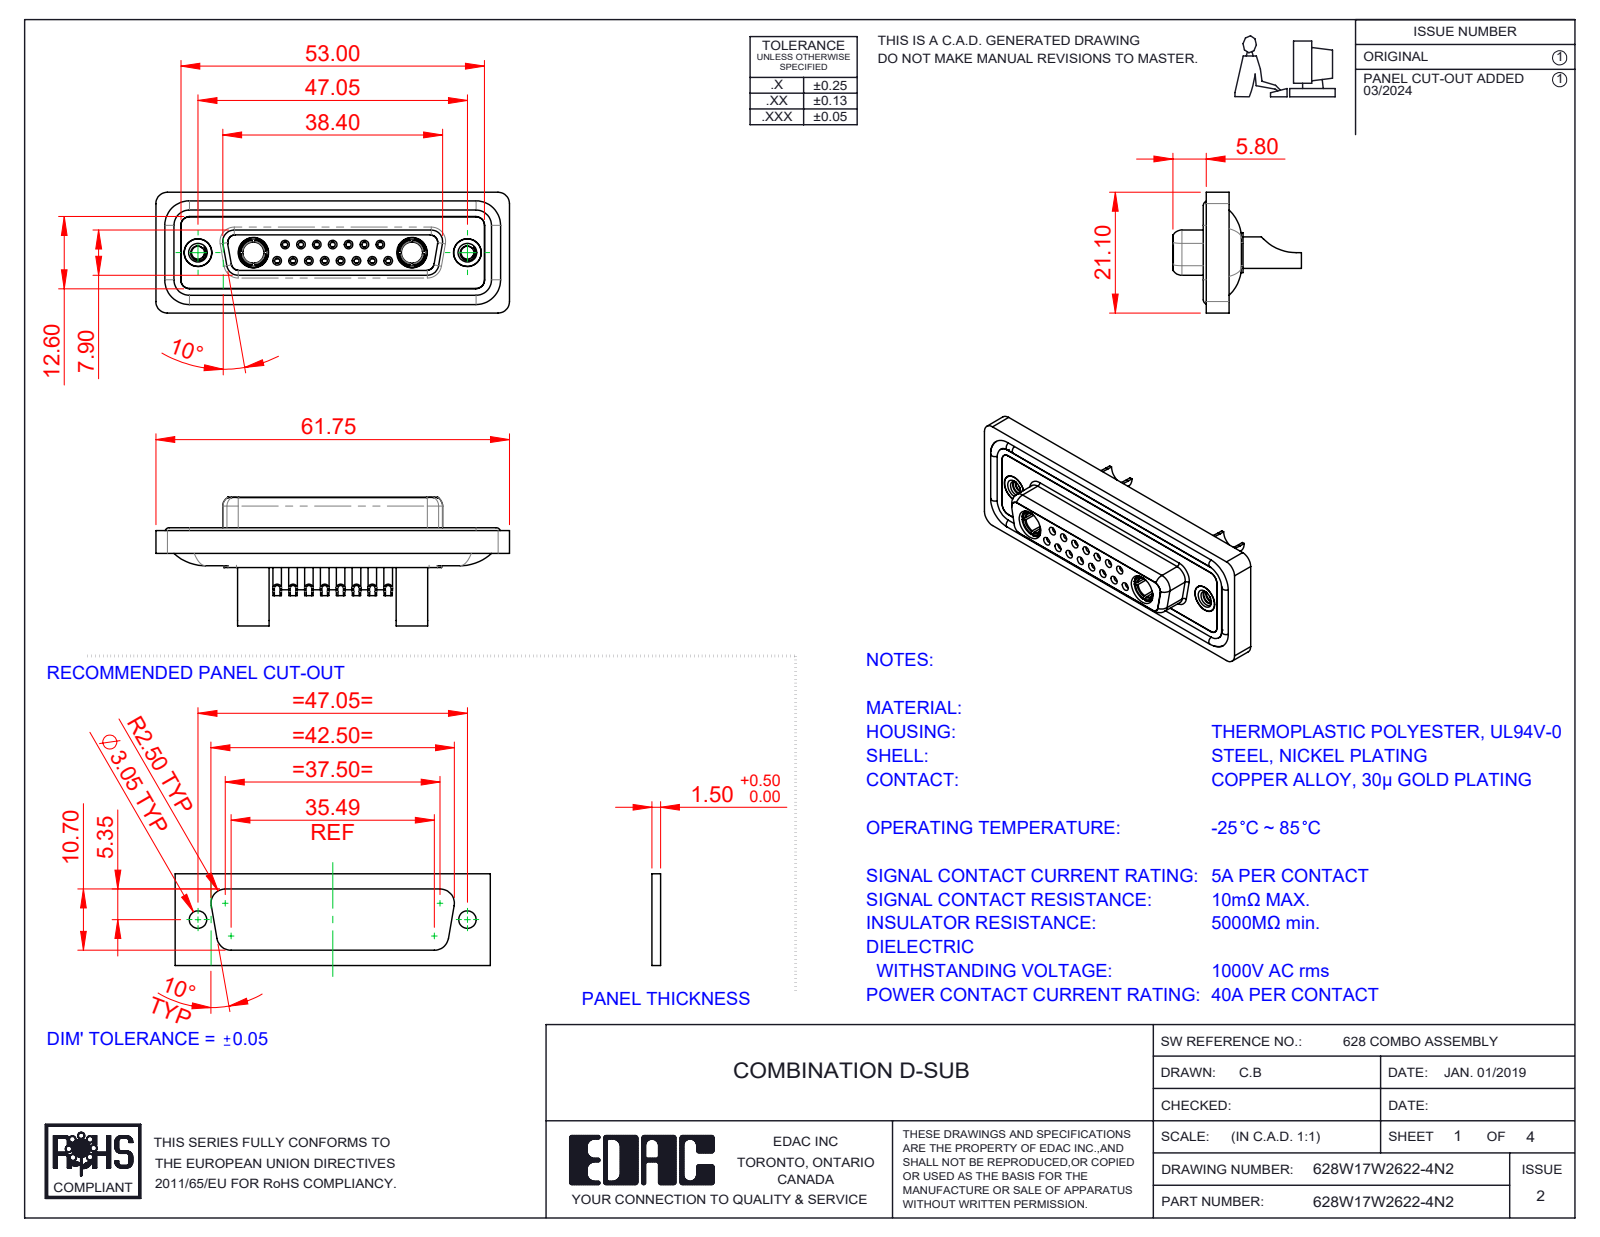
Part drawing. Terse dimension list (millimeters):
name: 628W17W2622-4N2; Power Socket_40A SC; 628Combo Shell Front_25 Contacts; 628Combo Waterproof Housing_25 Contacts (+5 more)
written by: SolidWorks 2023 (CONFIG_CONTROL_DESIGN)
unit: mm
bodies: 26 solids, 1365 faces (422 planar, 551 cylindrical, 392 other)
size: 61.75 × 22.45 × 21.1
volume: 8 435 mm³; area: 14 295 mm²
holes: 15× ⌀0.9, 15× ⌀1, 15× ⌀1.1, 15× ⌀1.5, 15× ⌀2, 8× ⌀1.6, 7× ⌀1.7, 4× ⌀4.85, 2× ⌀2.26, 2× ⌀3.7, 2× ⌀4, 2× ⌀4.05
bosses: 15× ⌀2.2, 11× ⌀1.6, 2× ⌀5.5, 2× ⌀5.2, 2× ⌀4.96, 2× ⌀4.95, 2× ⌀4.8, 2× ⌀4.75
rounds: 22× R1.5, 18× R2, 8× R1.35, 8× R1.6, 6× R1, 4× R0.25, 4× R0.5, 4× R0.6
face distances: 0.4, 7.45, 1.8, 5.65, 6.6, 0.5, 7.05, 1.6, 2.9, 1.1
hole spacings: 3.16, 2.77, 8.31, 5.54, 5.03, 5.04, 7.49, 11.08
